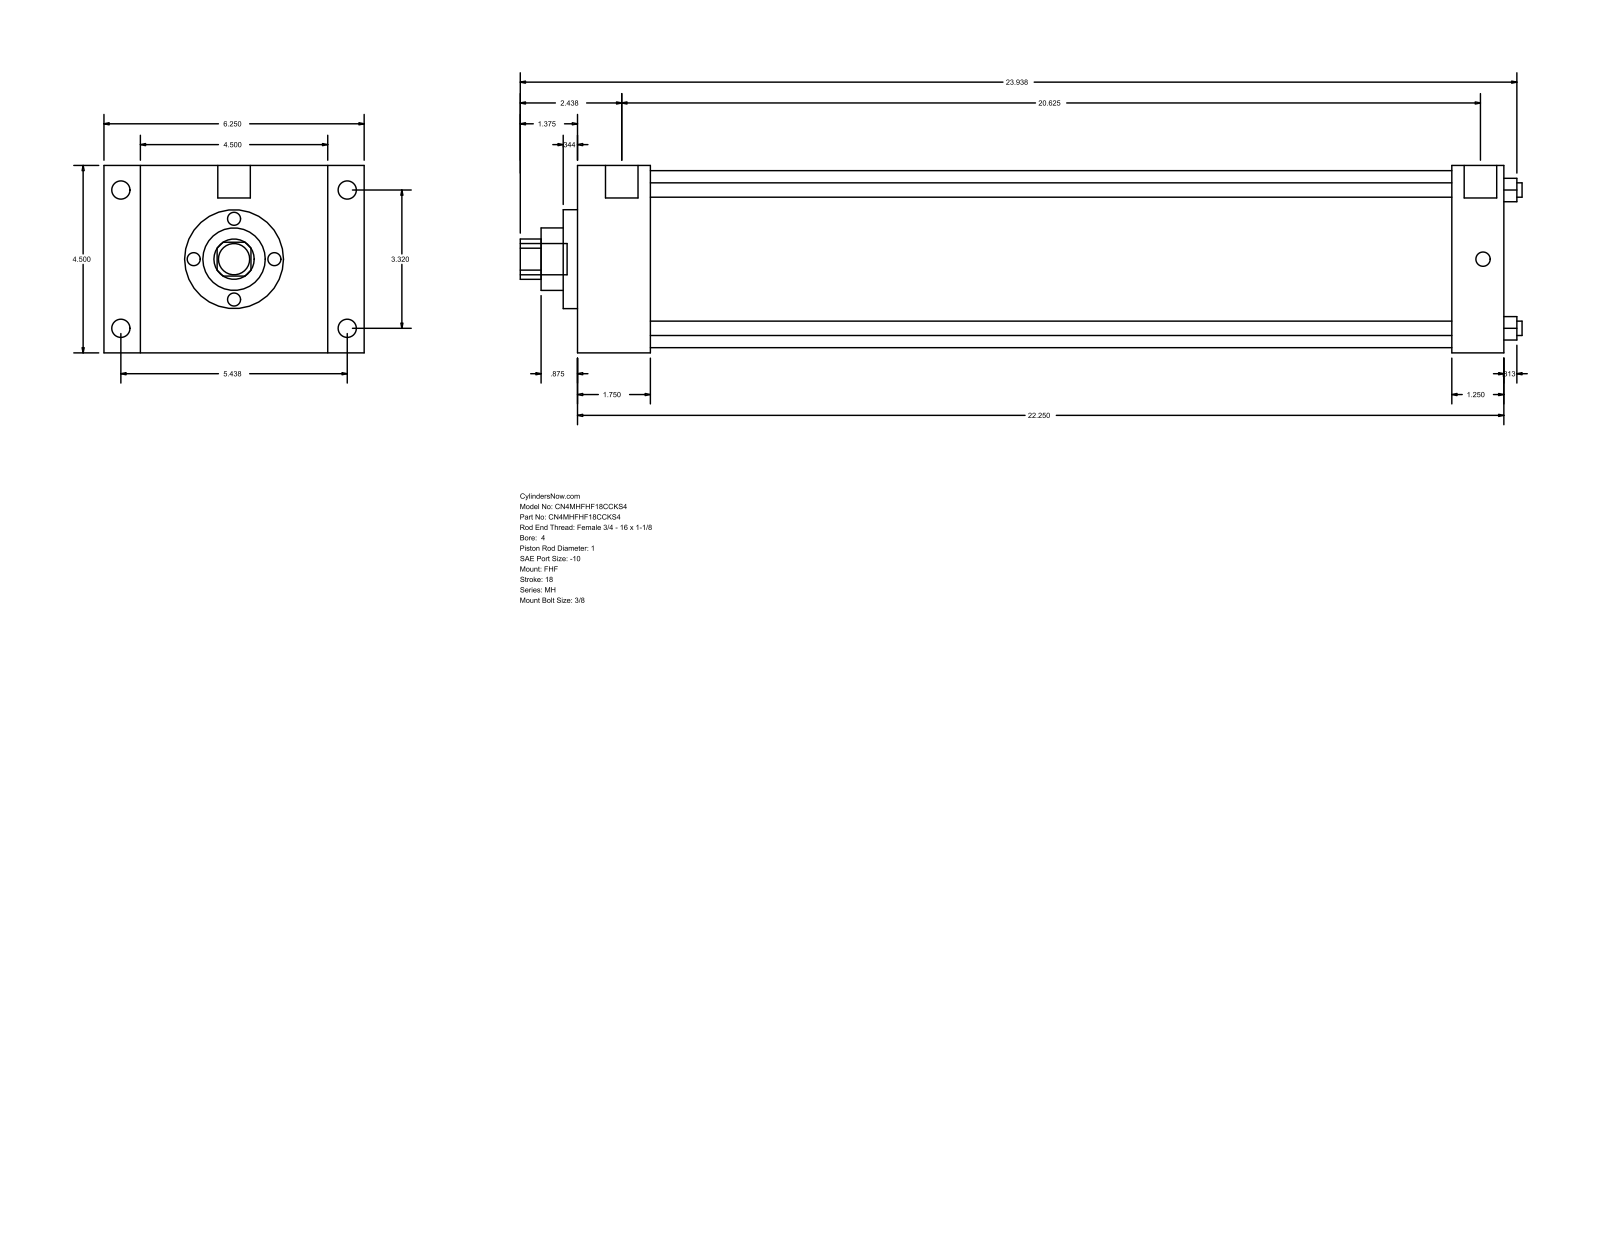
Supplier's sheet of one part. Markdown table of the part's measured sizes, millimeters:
| quantity | value |
| --- | --- |
| part name | MH_FHF__0400_1 |
| STEP written by | GSSL Pune (CONFIG_CONTROL_DESIGN) |
| units | millimeters |
| bodies | 0 solids, 90 faces (61 planar, 29 cylindrical, 0 other) |
| overall size | 611.19 × 158.75 × 114.3 |
| round holes (diameter × count) | 8.76 × 4, 25.4 × 1, 38.1 × 1, 60.33 × 1, 107.95 × 1 |
| round bosses / shafts (diameter × count) | 11.13 × 4, 8.73 × 4, 19.84 × 2, 19.05 × 1 |
| partial cylindrical surfaces (radius × count) | 12.29 × 1 |
| main face-to-face distances | 114.3, 565.16, 44.46, 520.7, 22.23, 136.53, 158.76, 533.41, 488.95, 31.75 |
| hole center spacings | 59.62, 84.32, 119.25 |
